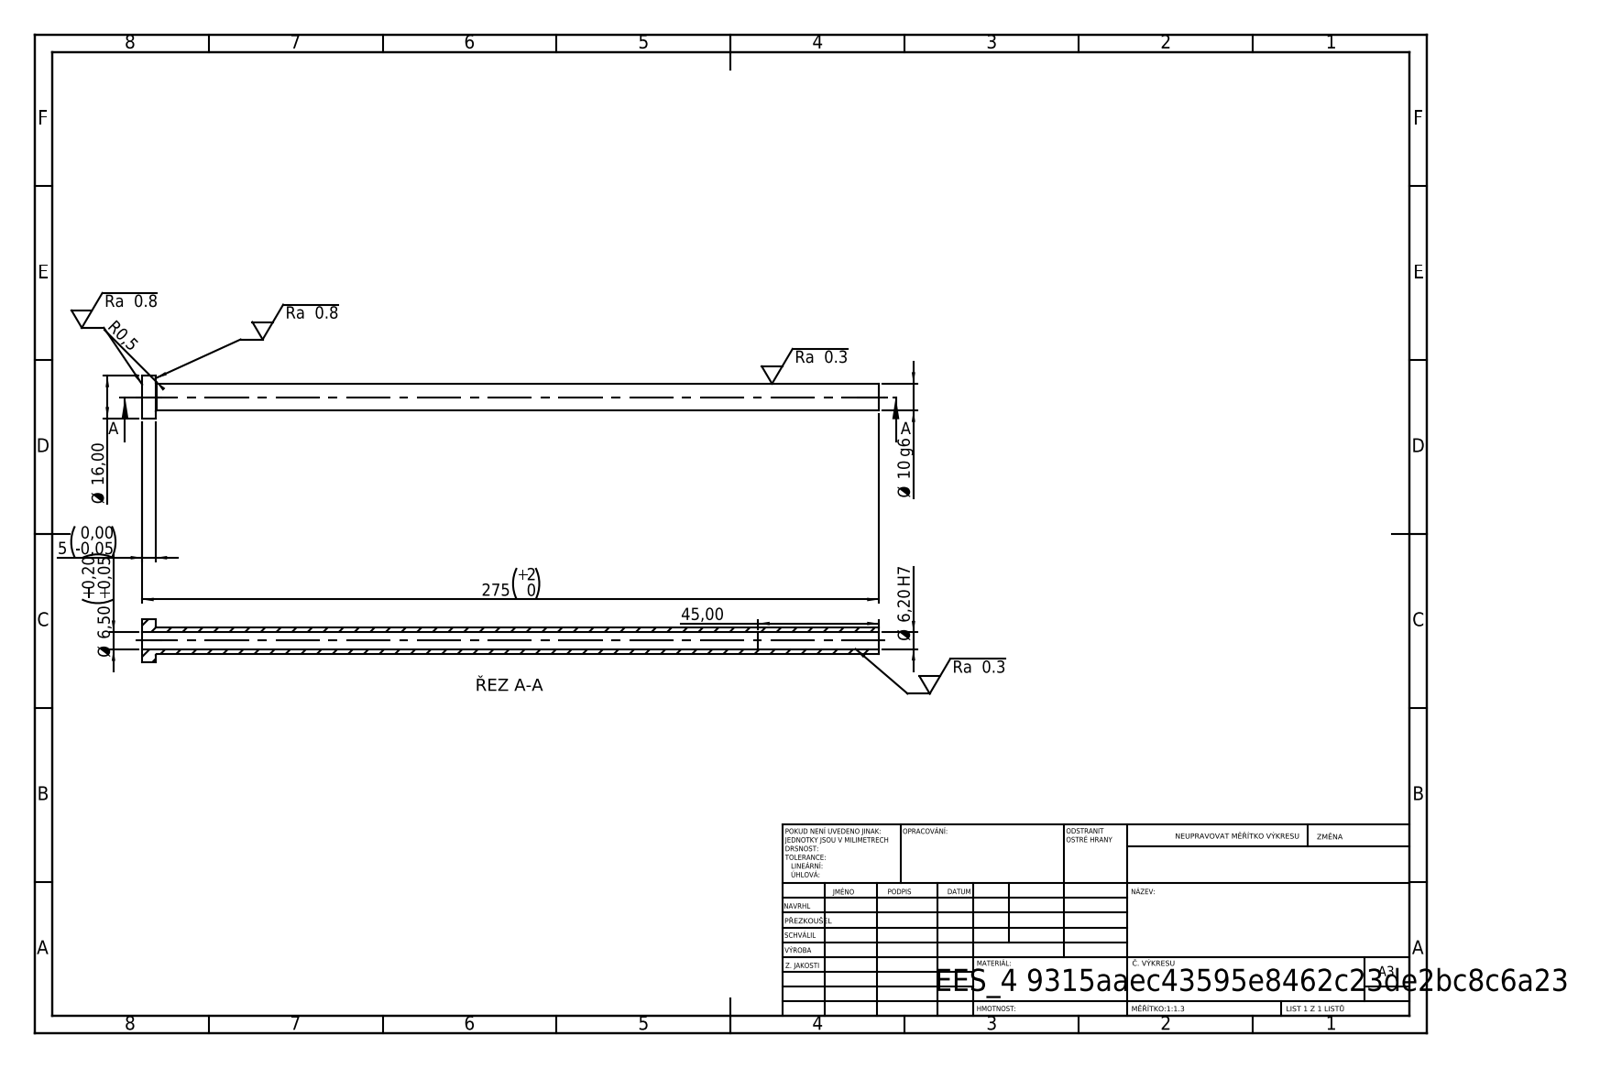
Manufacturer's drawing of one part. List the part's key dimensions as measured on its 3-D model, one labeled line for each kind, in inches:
STEP written by: SolidWorks 2019 (CONFIG_CONTROL_DESIGN)
Units: inches
Bodies: 1 solid, 14 faces (4 planar, 8 cylindrical, 2 other)
Overall size (bounding box): 10.827 × 0.63 × 0.63
Volume: 0.807 in³ · Surface area: 22.7 in²
Round holes (diameter × count): ⌀0.244 ×1, ⌀0.256 ×1
Round bosses / shafts (diameter × count): ⌀0.63 ×1, ⌀0.394 ×1
Main face-to-face distances: 0.197, 10.827, 10.63, 9.055, 8.858, 1.772
